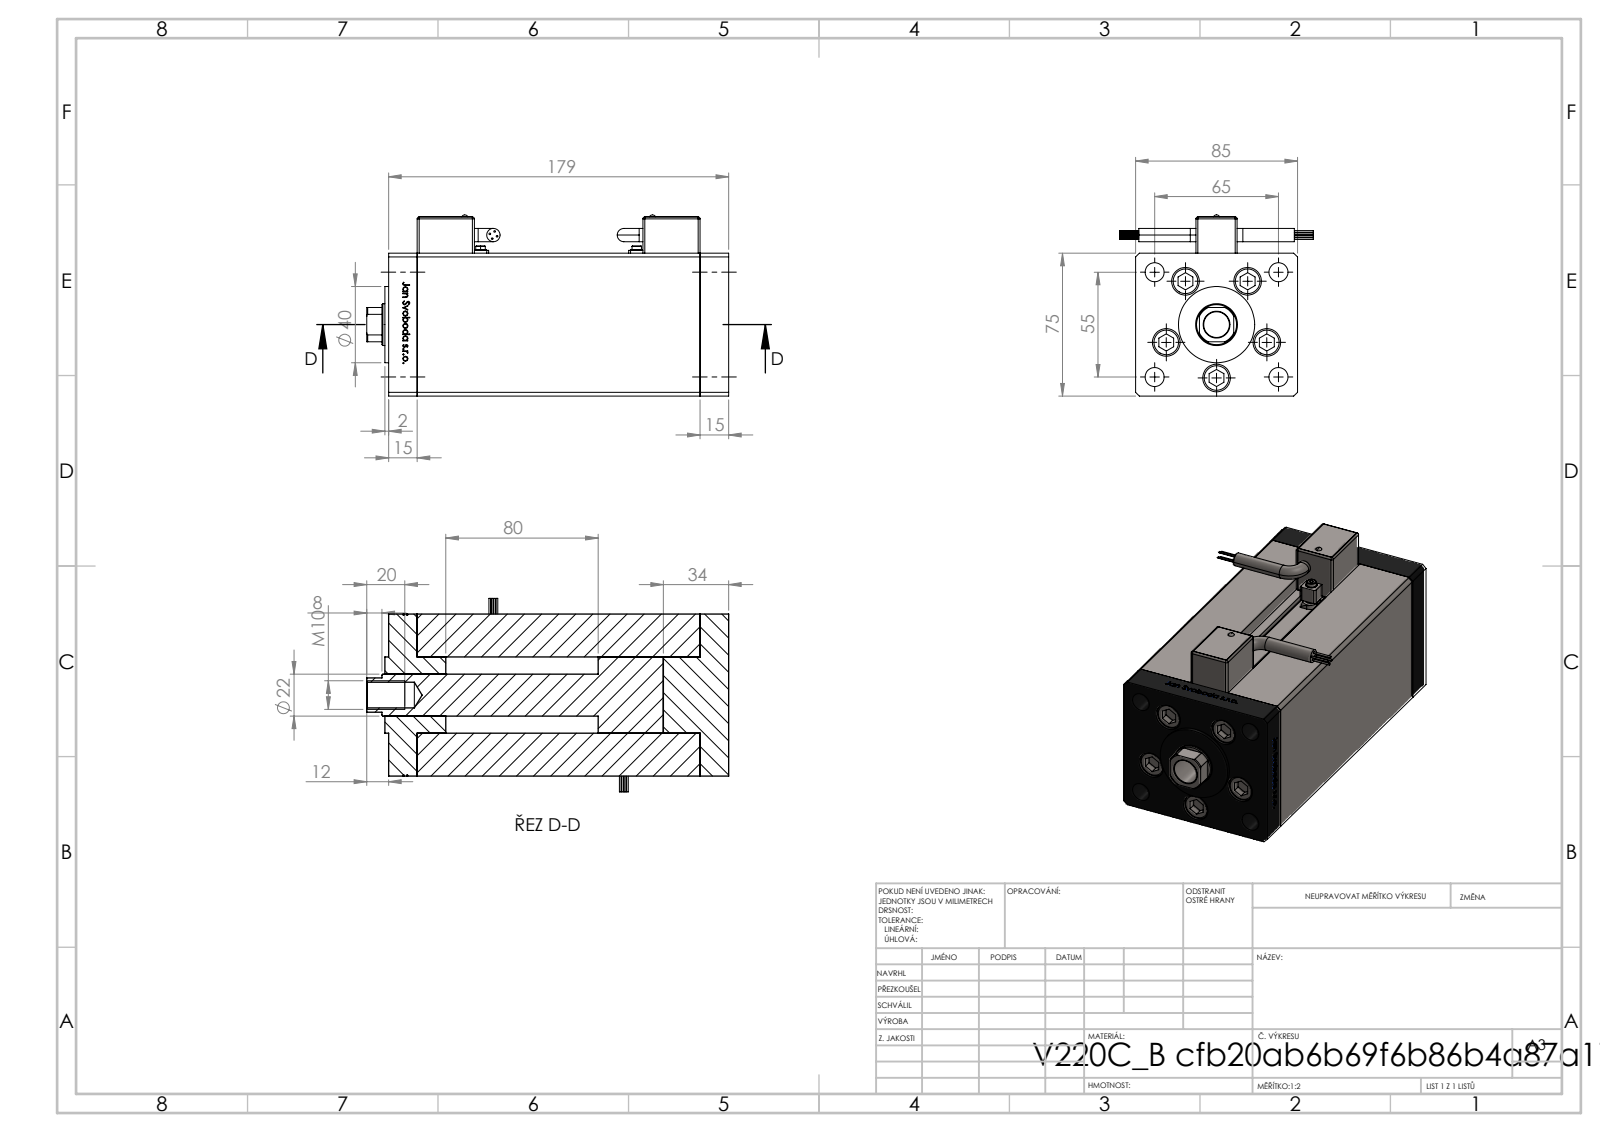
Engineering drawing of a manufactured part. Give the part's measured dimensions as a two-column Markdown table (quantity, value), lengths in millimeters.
| quantity | value |
| --- | --- |
| part name | Magnetic_Switch_MSU4; ALLEN BOLT; V220C BACK_B; V220C_FRONT_B (+2 more) |
| STEP written by | SolidWorks 2019 (CONFIG_CONTROL_DESIGN) |
| units | millimeters |
| bodies | 16 solids, 1389 faces (542 planar, 237 cylindrical, 610 other) |
| overall size | 190 × 101.6 × 95.1 |
| volume | 1 049 000 mm³ |
| surface area | 171 822 mm² |
| round holes (diameter × count) | 11 × 5, 14.5 × 5, 10 × 4, 2 × 2, 3.6 × 2, 5 × 2, 7 × 2, 13.16 × 2, 13.5 × 1, 22 × 1 |
| round bosses / shafts (diameter × count) | 0.85 × 8, 8 × 5, 7 × 4, 6 × 2, 3.5 × 2, 2.5 × 2, 40 × 1 |
| partial cylindrical surfaces (radius × count) | 1 × 24, 4 × 4, 0.93 × 2, 10.5 × 1 |
| main face-to-face distances | 85, 75, 15, 148.5, 163.5, 178.5, 68.5, 34.25, 6.5, 31.7 |
| hole center spacings | 28, 42.57, 8.25, 16.86, 19.17, 32.33, 32.5, 33.63 |
